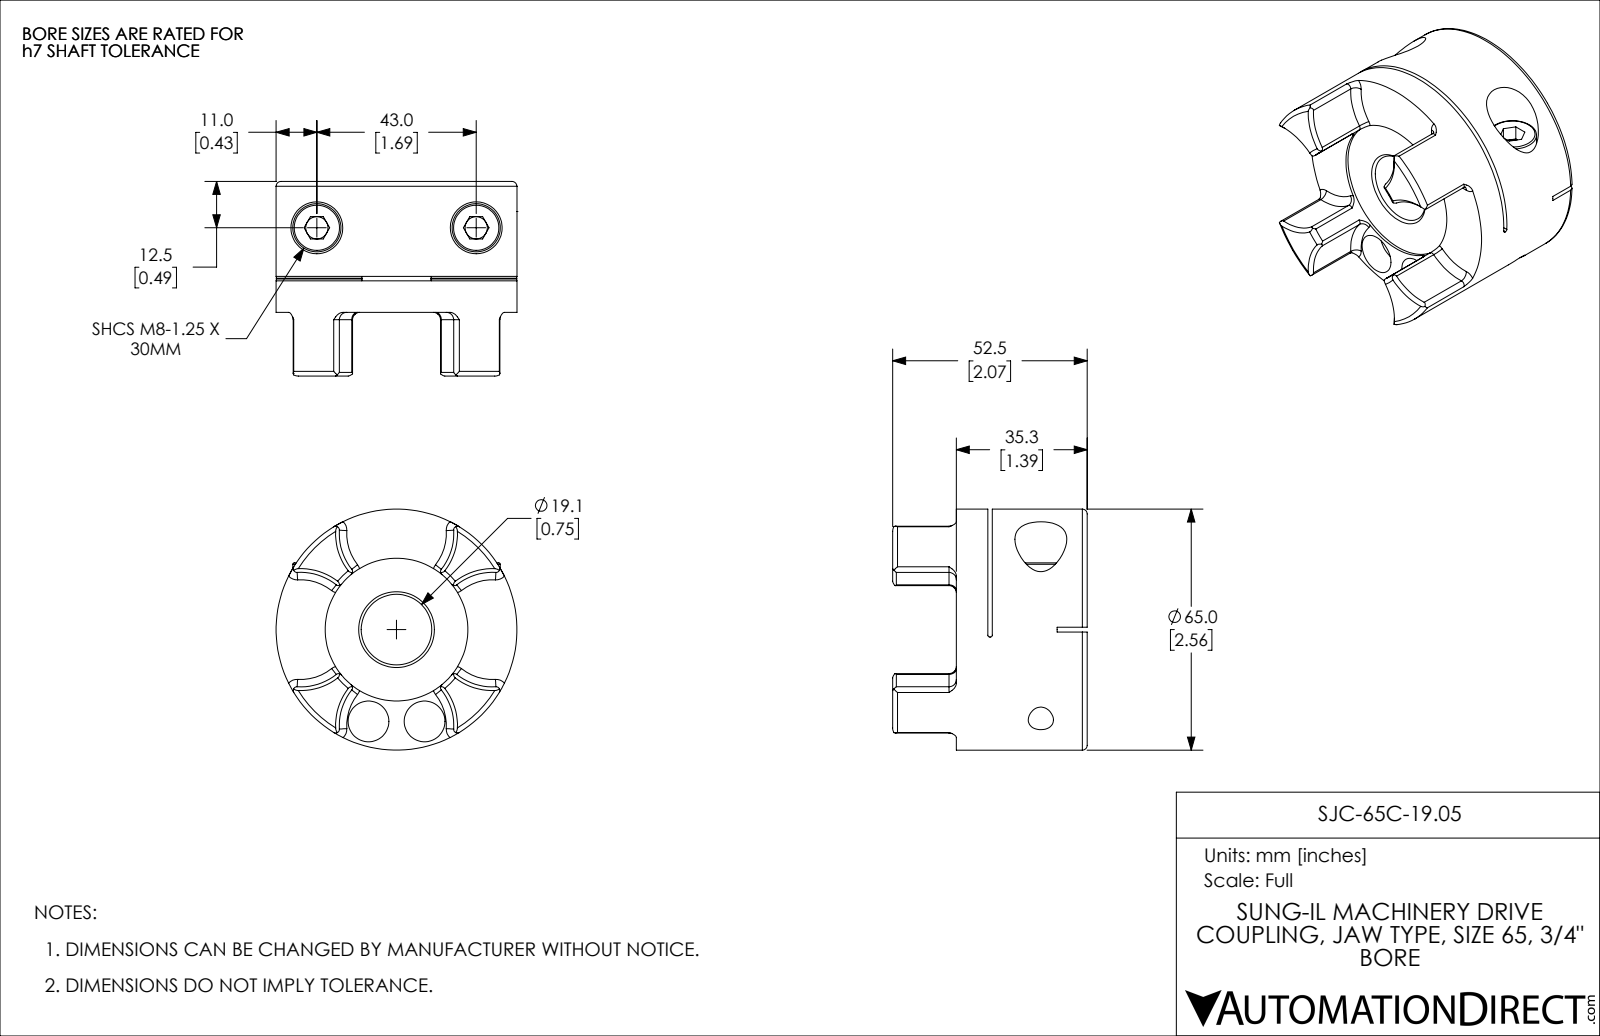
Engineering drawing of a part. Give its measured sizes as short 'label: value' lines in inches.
name: SJC-65C-19.05
written by: SolidWorks 2021 (CONFIG_CONTROL_DESIGN)
unit: in
bodies: 3 solids, 216 faces (52 planar, 77 cylindrical, 87 other)
size: 2.559 × 2.559 × 2.067
volume: 6.624 in³; area: 44.78 in²
holes: 2× ⌀0.236, 2× ⌀0.268, 2× ⌀0.335, 2× ⌀0.433, 2× ⌀0.551, 1× ⌀0.75, 1× ⌀1.516
bosses: 2× ⌀0.512, 2× ⌀0.315, 1× ⌀2.559
rounds: 16× R0.039, 4× R0.608, 2× R0.02, 1× R1.969
face distances: 1.055, 0.047, 1.008, 0.335, 0.382, 1.39, 0.051, 0.031, 0.303, 0.35
hole spacings: 1.019, 0.596, 1.693
